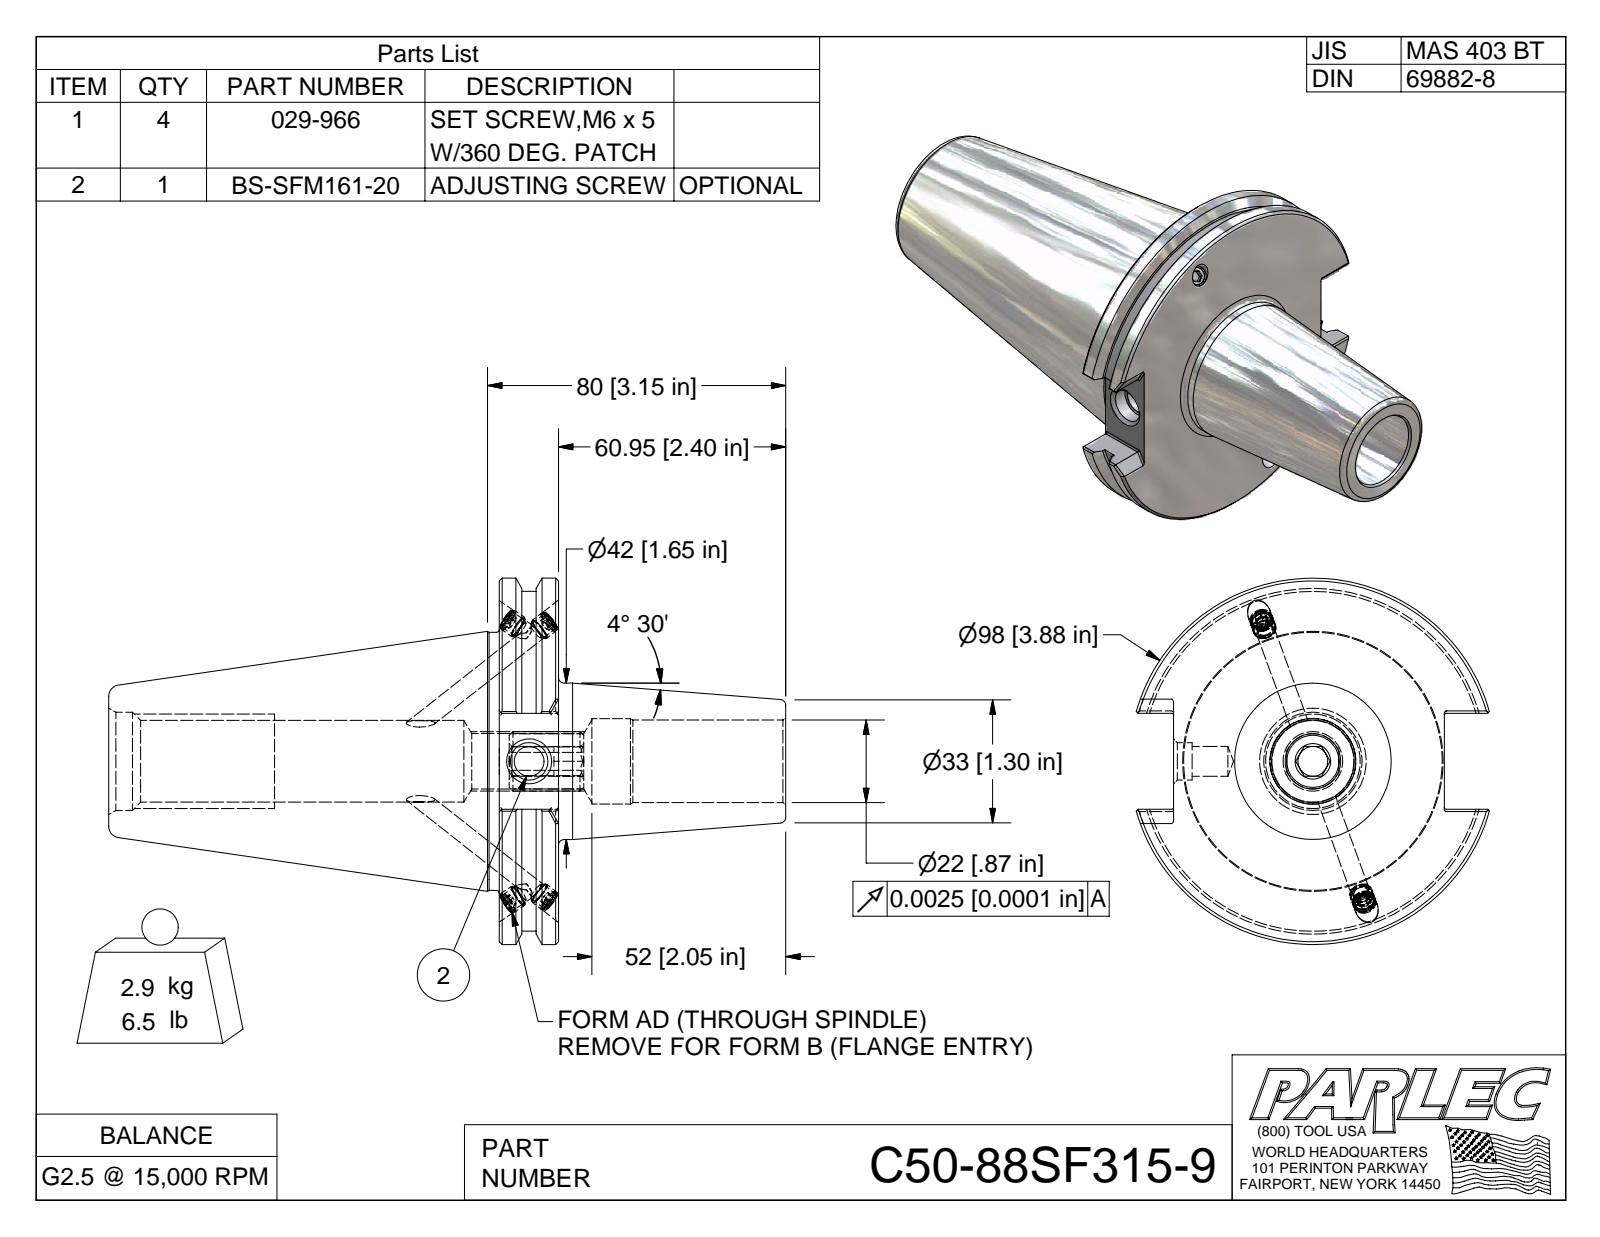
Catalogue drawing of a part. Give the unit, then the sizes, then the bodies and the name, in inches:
Units: inches
Overall size (bounding box): 7.15 × 3.875 × 3.729
Round holes (diameter × count): ⌀0.197 ×4, ⌀0.24 ×4, ⌀0.874 ×1, ⌀0.904 ×1
Round bosses / shafts (diameter × count): ⌀0.244 ×4, ⌀0.236 ×4, ⌀3.875 ×1, ⌀3.594 ×1, ⌀2.73 ×1, ⌀1.654 ×1
Partial cylindrical surfaces — rounded edges, fillets, slot ends (radius × count): R0.02 ×12, R0.315 ×1
Main face-to-face distances: 0.625, 4.125, 4.75, 7.15, 3.025, 2.4, 2.86, 1.015, 4.363, 0.238
Volume: 22.56 in³ · Surface area: 90.28 in²
Bodies: 6 solids, 184 faces (87 planar, 44 cylindrical, 53 other)
Part name (STEP PRODUCT): C50-88SF315-9; C50BC-88SF315-9-1; BS-SFM161-20; 029-966
STEP written by: Autodesk Inventor 2009 (AUTOMOTIVE_DESIGN)
